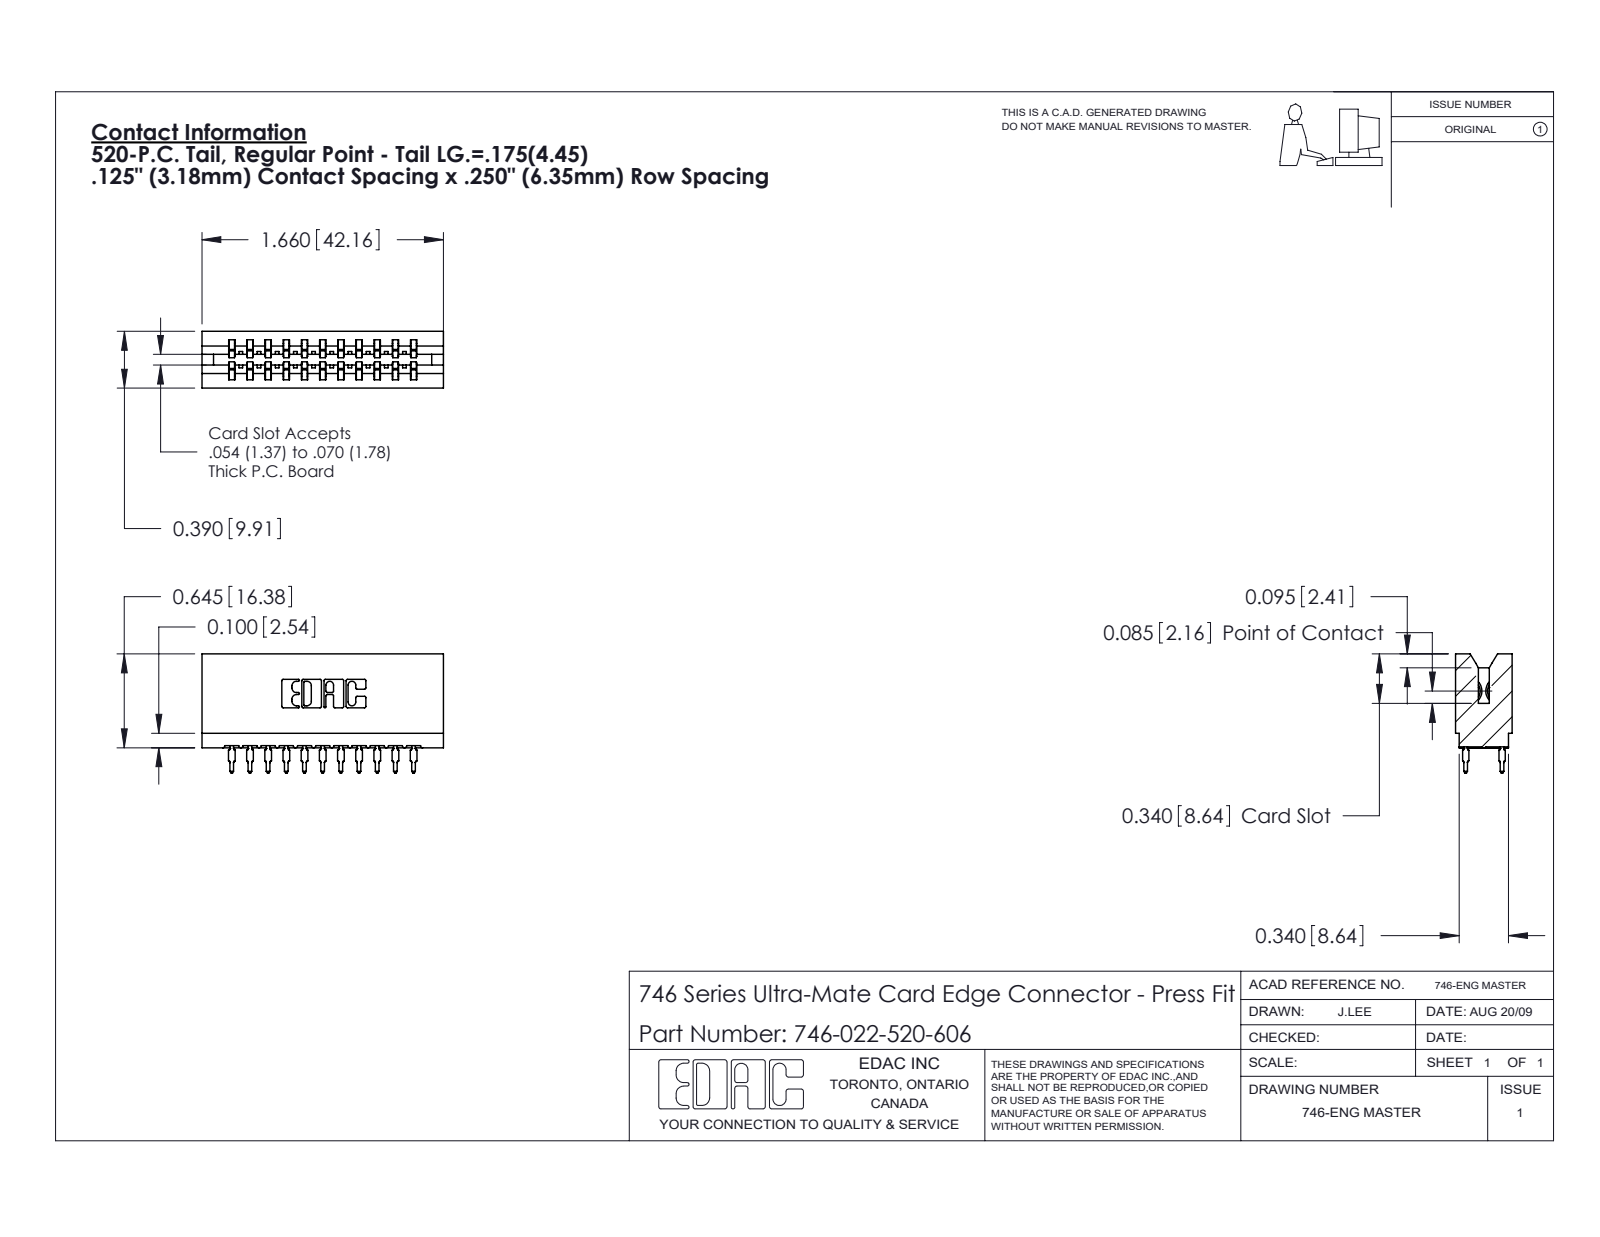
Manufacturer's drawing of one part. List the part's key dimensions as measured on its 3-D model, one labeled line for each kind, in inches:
Part name (STEP PRODUCT): 746-292-001_520; 746-022-520-606; 746 Part_.340 Slot Depth - 06
STEP written by: SolidWorks 2020 (CONFIG_CONTROL_DESIGN)
Units: inches
Bodies: 23 solids, 2067 faces (1068 planar, 427 cylindrical, 572 other)
Overall size (bounding box): 1.66 × 0.819 × 0.39
Volume: 0.304 in³ · Surface area: 10.3 in²
Partial cylindrical surfaces — rounded edges, fillets, slot ends (radius × count): R0.021 ×44, R0.01 ×22, R0.015 ×12, R0.005 ×8, R0.011 ×8, R0.007 ×6, R0.031 ×6, R0.026 ×3
Main face-to-face distances: 0.25, 0.333, 0.5, 0.057, 0.125, 0.042, 0.125, 0.292, 0.542, 0.39
